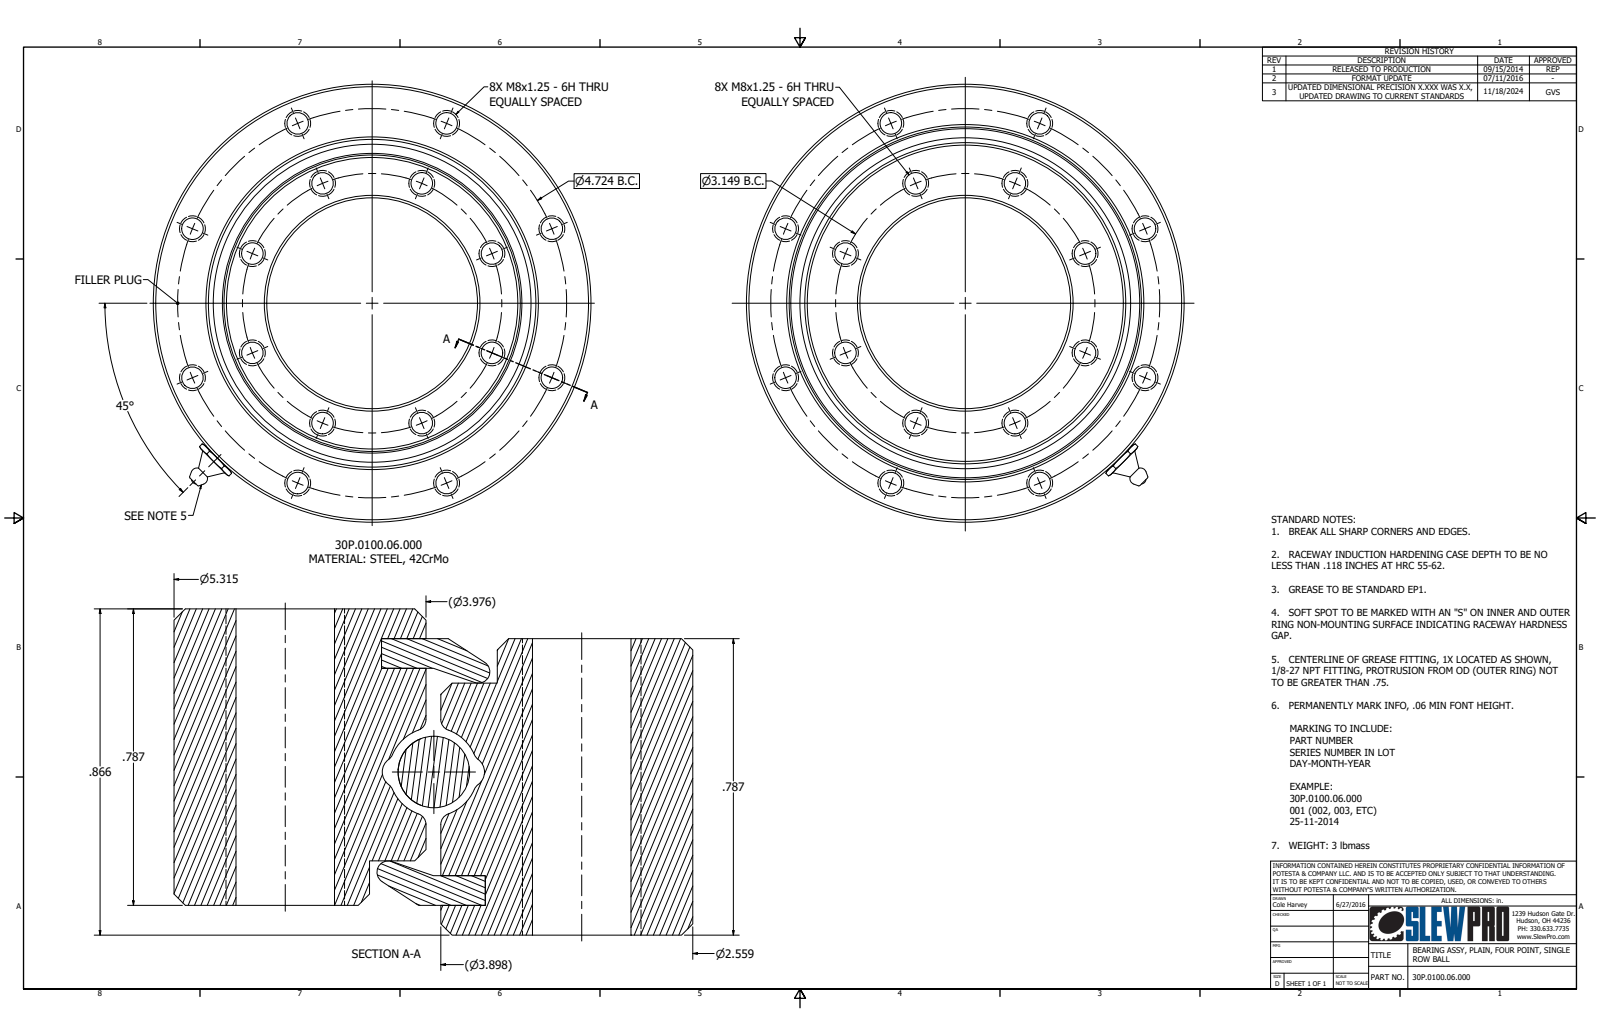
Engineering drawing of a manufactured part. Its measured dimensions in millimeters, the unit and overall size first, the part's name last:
Units: millimetres
Overall size (bounding box): 135 × 135 × 22
Round holes (diameter × count): ⌀6.7 ×16, ⌀2.5 ×1, ⌀8.5 ×1, ⌀65 ×1, ⌀93 ×1, ⌀101 ×1, ⌀107 ×1, ⌀108.6 ×1
Round bosses / shafts (diameter × count): ⌀135 ×1, ⌀99 ×1, ⌀91.4 ×1
Main face-to-face distances: 20, 2, 18, 4, 18, 2, 16, 22, 14, 5
Hole centre spacings: 20, 40, 42.5, 42.5, 45.9, 56.6, 60, 72.1
Volume: 199 600 mm³ · Surface area: 78 390 mm²
Bodies: 94 solids, 292 faces (25 planar, 37 cylindrical, 230 other)
Part name (STEP PRODUCT): 30P.0100.06.000; 1_8 NPT Fitting
STEP written by: Autodesk Inventor 2024 (AUTOMOTIVE_DESIGN)
